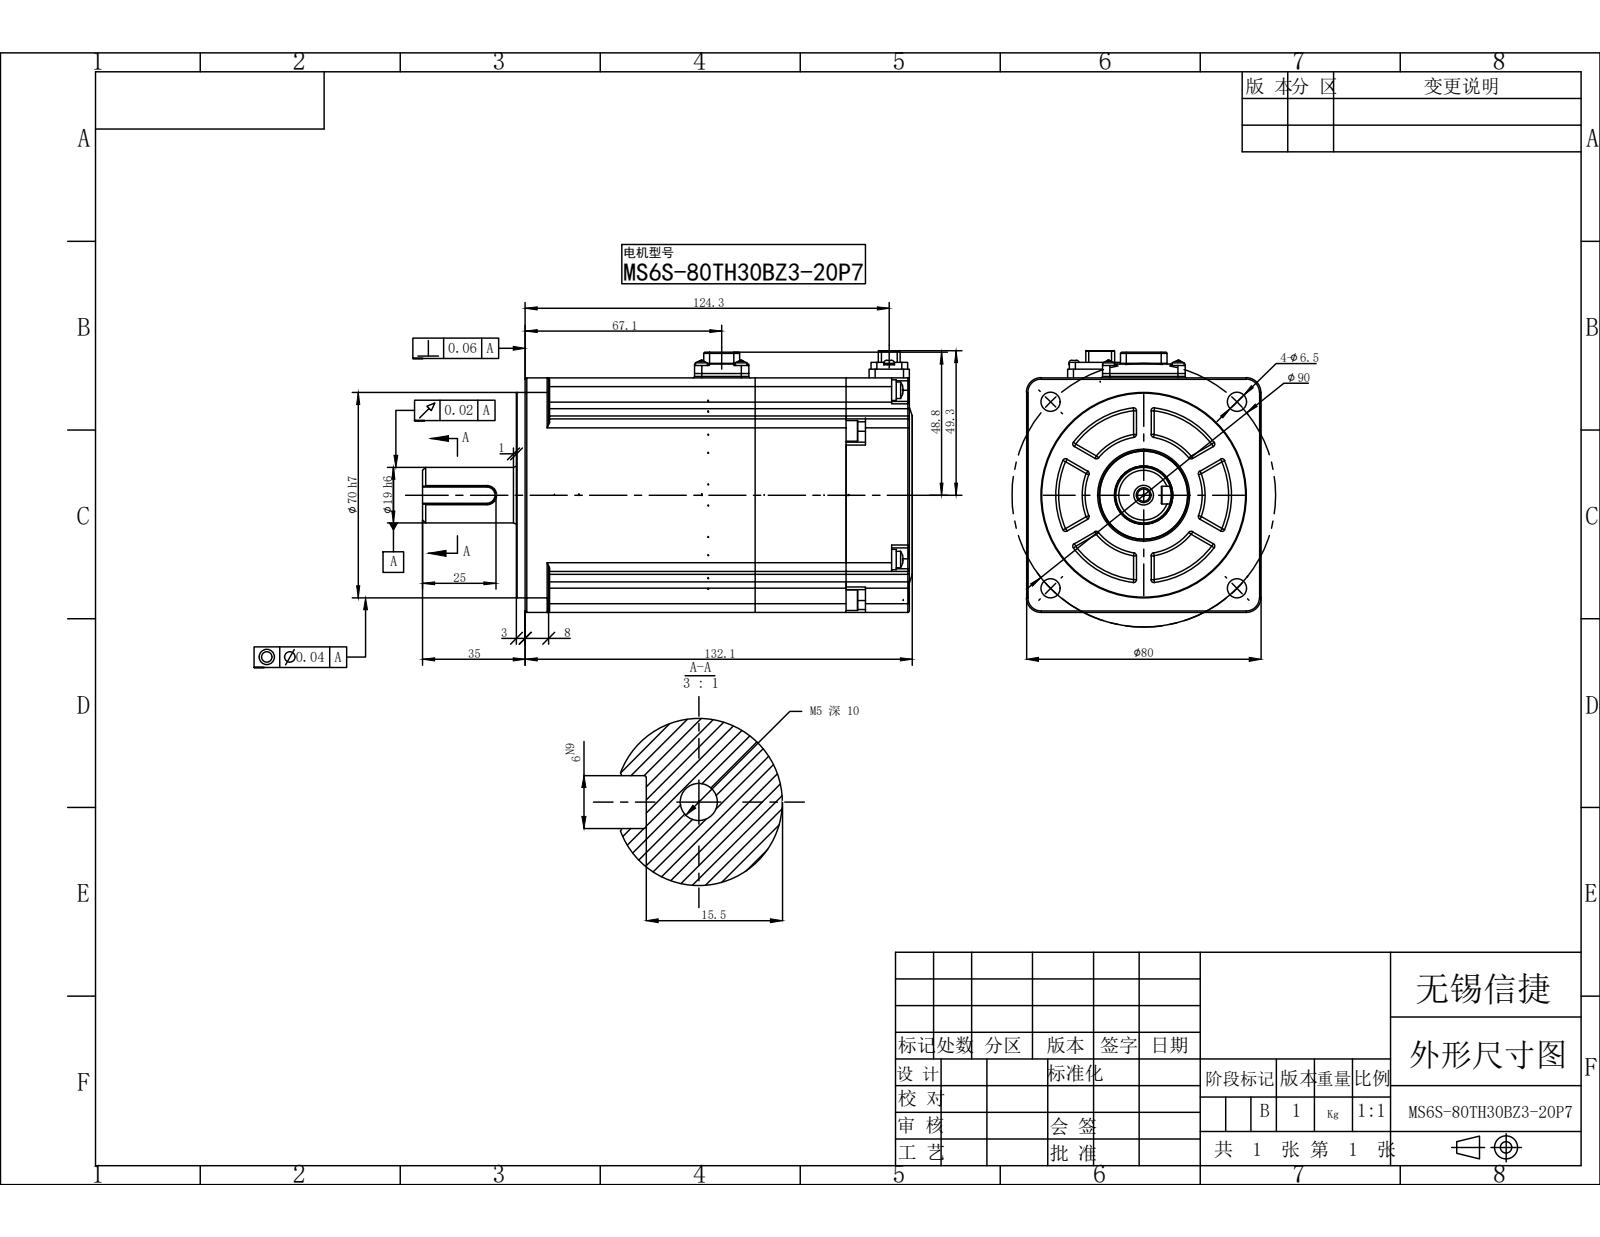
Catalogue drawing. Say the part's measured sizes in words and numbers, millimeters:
The part is named "MS6S-80TH30BZ3-20P7". Its 3-D file was written by "SolidWorks 2022 (CONFIG_CONTROL_DESIGN)". It is 0 solids with 881 faces: 377 planar, 318 cylindrical and 186 other. Overall it measures 167.1 by 89.3 by 80 millimeters. Round holes: 4 of diameter 2.1, 4 of diameter 6.5, 2 of diameter 1.6, 1 of diameter 4.2, 1 of diameter 20. Round bosses or shafts: 8 of diameter 7, 4 of diameter 5.6, 4 of diameter 4, 2 of diameter 3.5, 1 of diameter 70, 1 of diameter 30, 1 of diameter 19.8, 1 of diameter 19. Partial cylindrical surfaces (rounded edges, fillets, slot ends): 50 of radius 1, 39 of radius 0.5, 17 of radius 3, 15 of radius 0.2, 14 of radius 0.3, 12 of radius 2, 8 of radius 3.75, 4 of radius 0.6. The main face-to-face distances are 80, 14, 66, 131.1, 52, 1, 132.1, 3, 135.1, 134.1. The hole center spacings are 45, 63.64, 8, 16.6, 18.43, 90, 23.5, 53.45.
